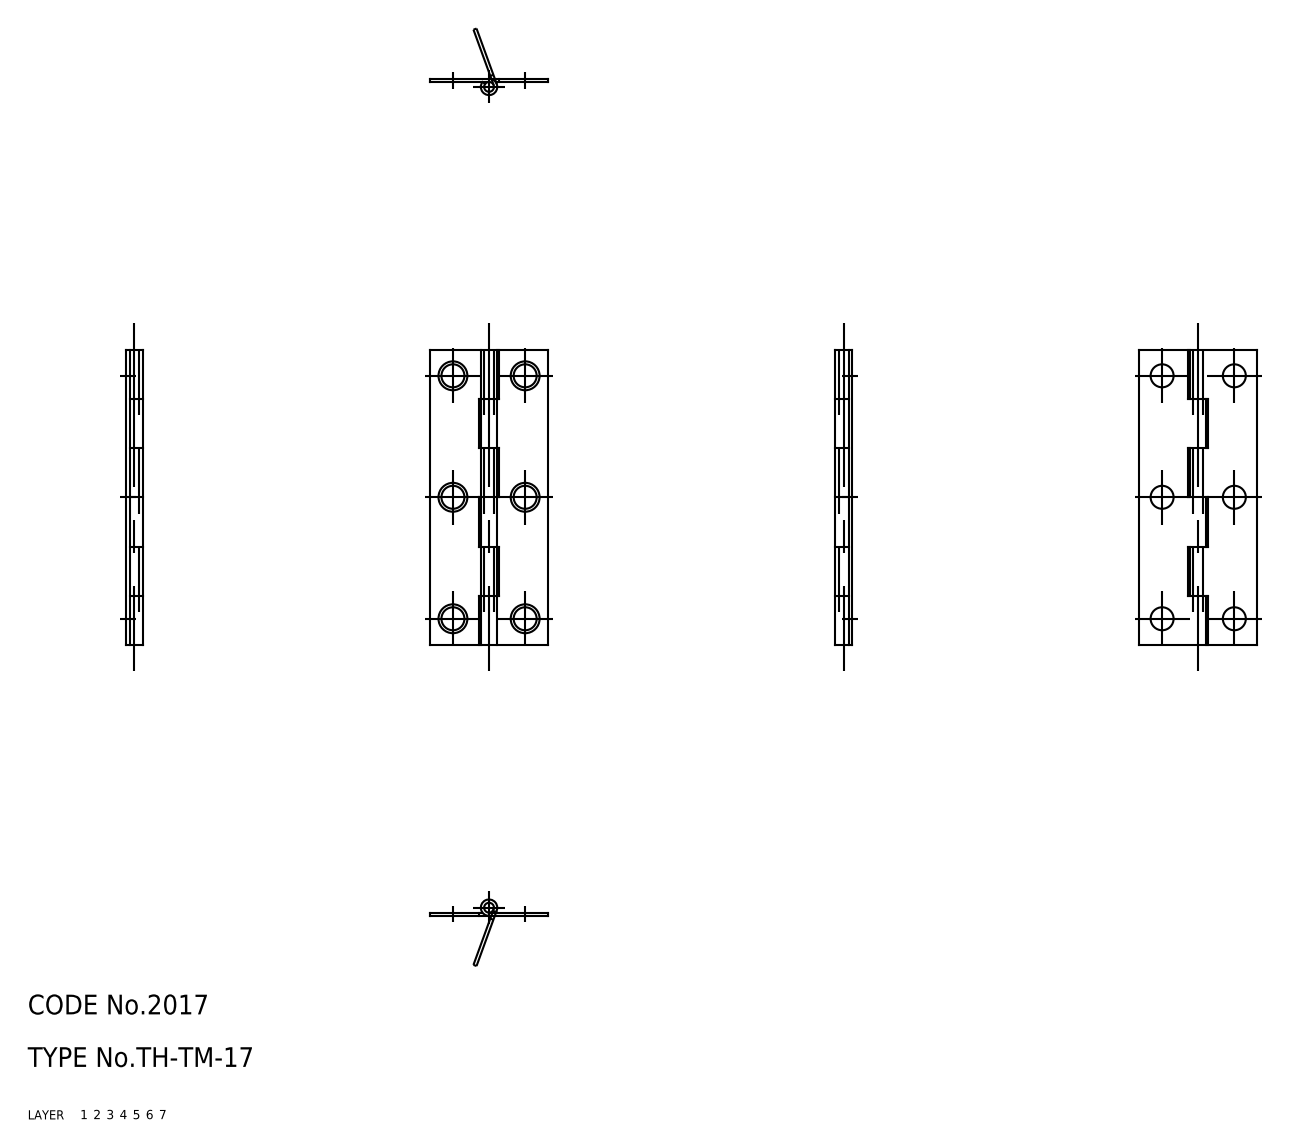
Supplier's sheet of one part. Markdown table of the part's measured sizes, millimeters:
| quantity | value |
| --- | --- |
| part name | shaft; hinge piece_B; hinge piece_A; TH_TM_17_21781_36 |
| STEP written by | CADfix (AUTOMOTIVE_DESIGN) |
| units | millimeters |
| bodies | 3 solids, 72 faces (0 planar, 0 cylindrical, 72 other) |
| overall size | 45 × 18 × 2.5 |
| volume | 534 mm³ |
| surface area | 2 226 mm² |
